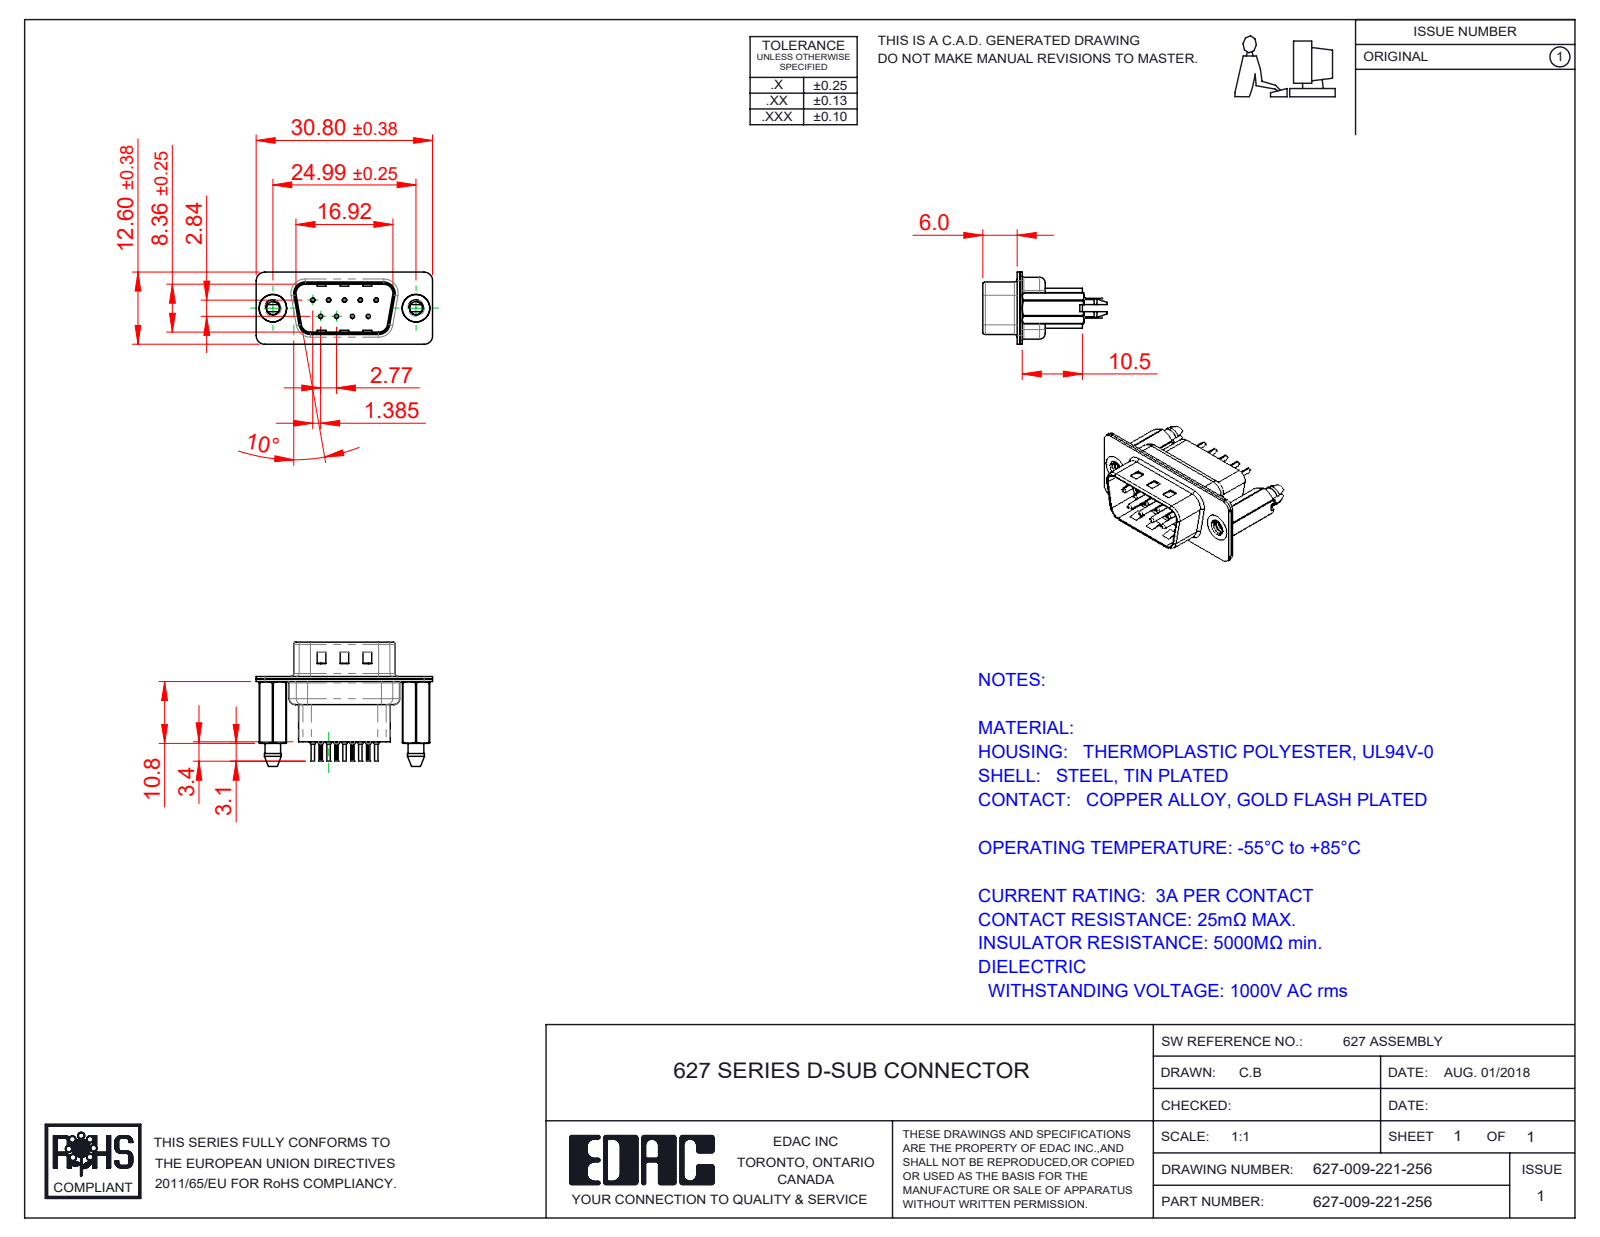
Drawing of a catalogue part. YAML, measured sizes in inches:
part_name: "627 Contact Row 1_21H; 627 Contact Row 2_21H; 627 Housing_09 HP; 627 4-40 Threaded Boardlock_HP (+3 more)"
step_written_by: "SolidWorks 2020 (CONFIG_CONTROL_DESIGN)"
units: inches
bodies: {solids: 14, faces: 1300, planar: 355, cylindrical: 530, other: 415}
overall_size: [1.213, 0.854, 0.496]
volume: 0.123
surface_area: 8.186
round_holes:
  - {diameter: 0.008, count: 9}
  - {diameter: 0.014, count: 9}
  - {diameter: 0.043, count: 9}
  - {diameter: 0.063, count: 9}
  - {diameter: 0.089, count: 2}
  - {diameter: 0.157, count: 2}
  - {diameter: 0.189, count: 2}
round_bosses_or_shafts:
  - {diameter: 0.079, count: 9}
  - {diameter: 0.059, count: 9}
  - {diameter: 0.03, count: 9}
  - {diameter: 0.024, count: 9}
  - {diameter: 0.193, count: 2}
partial_cylinders:
  - {radius: 0.059, count: 20}
  - {radius: 0.004, count: 18}
  - {radius: 0.079, count: 12}
  - {radius: 0.063, count: 10}
  - {radius: 0.02, count: 8}
  - {radius: 0.01, count: 4}
  - {radius: 0.024, count: 4}
  - {radius: 0.026, count: 4}
face_to_face_distances: [0.018, 0.016, 0.035, 0.032, 0.377, 0.055, 0.059, 0.027, 0.302, 0.043]
hole_center_spacings: [0.124, 0.109, 0.218, 0.198, 0.198, 0.327, 0.294, 0.295]
